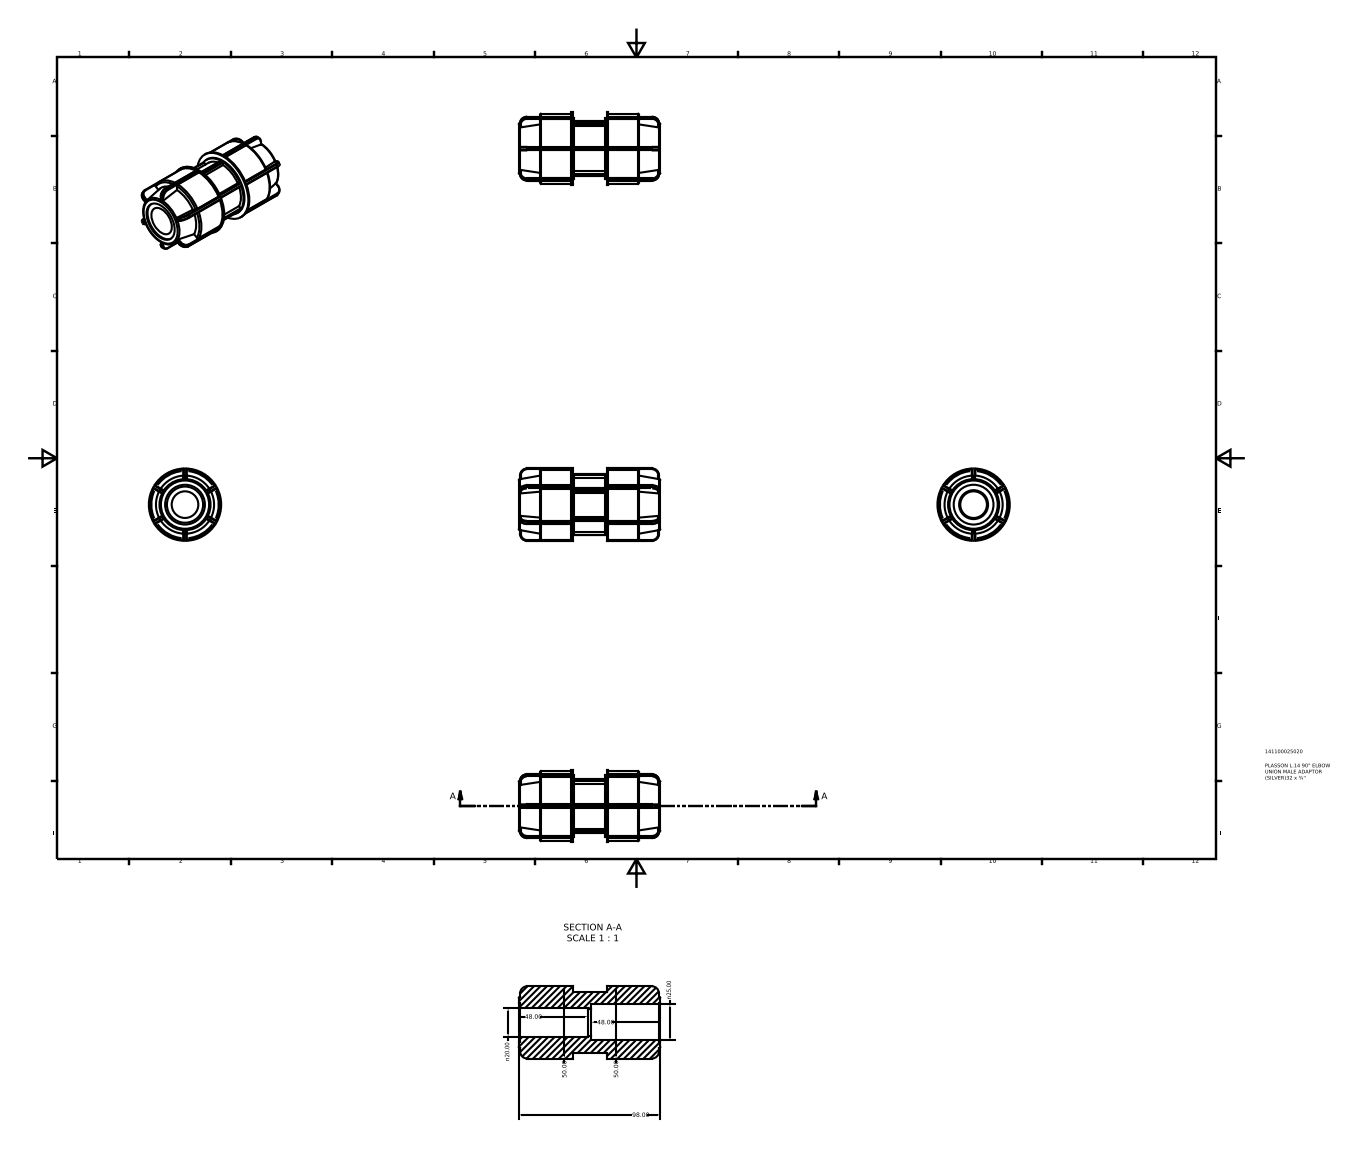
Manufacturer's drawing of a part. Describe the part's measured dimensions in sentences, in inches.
The part is named "141100025020". Its 3-D file was written by "Autodesk Inventor 2015 (AUTOMOTIVE_DESIGN)". It is 1 solid with 230 faces: 92 planar, 86 cylindrical and 52 other. Overall it measures 3.858 by 1.969 by 1.969 inches. Its volume is 6.514 cubic inches and its surface area 41.97 square inches. Round holes: 1 of diameter 0.724, 1 of diameter 0.787, 1 of diameter 0.984, 1 of diameter 1.083. Round bosses or shafts: 1 of diameter 1.969, 1 of diameter 1.909, 1 of diameter 1.673, 1 of diameter 1.476. Partial cylindrical surfaces (rounded edges, fillets, slot ends): 44 of radius 0.02. The main face-to-face distances are 0.887, 0.926, 0.098, 0.039, 2.354, 1.466, 1.813, 2.392, 1.428, 0.579.
